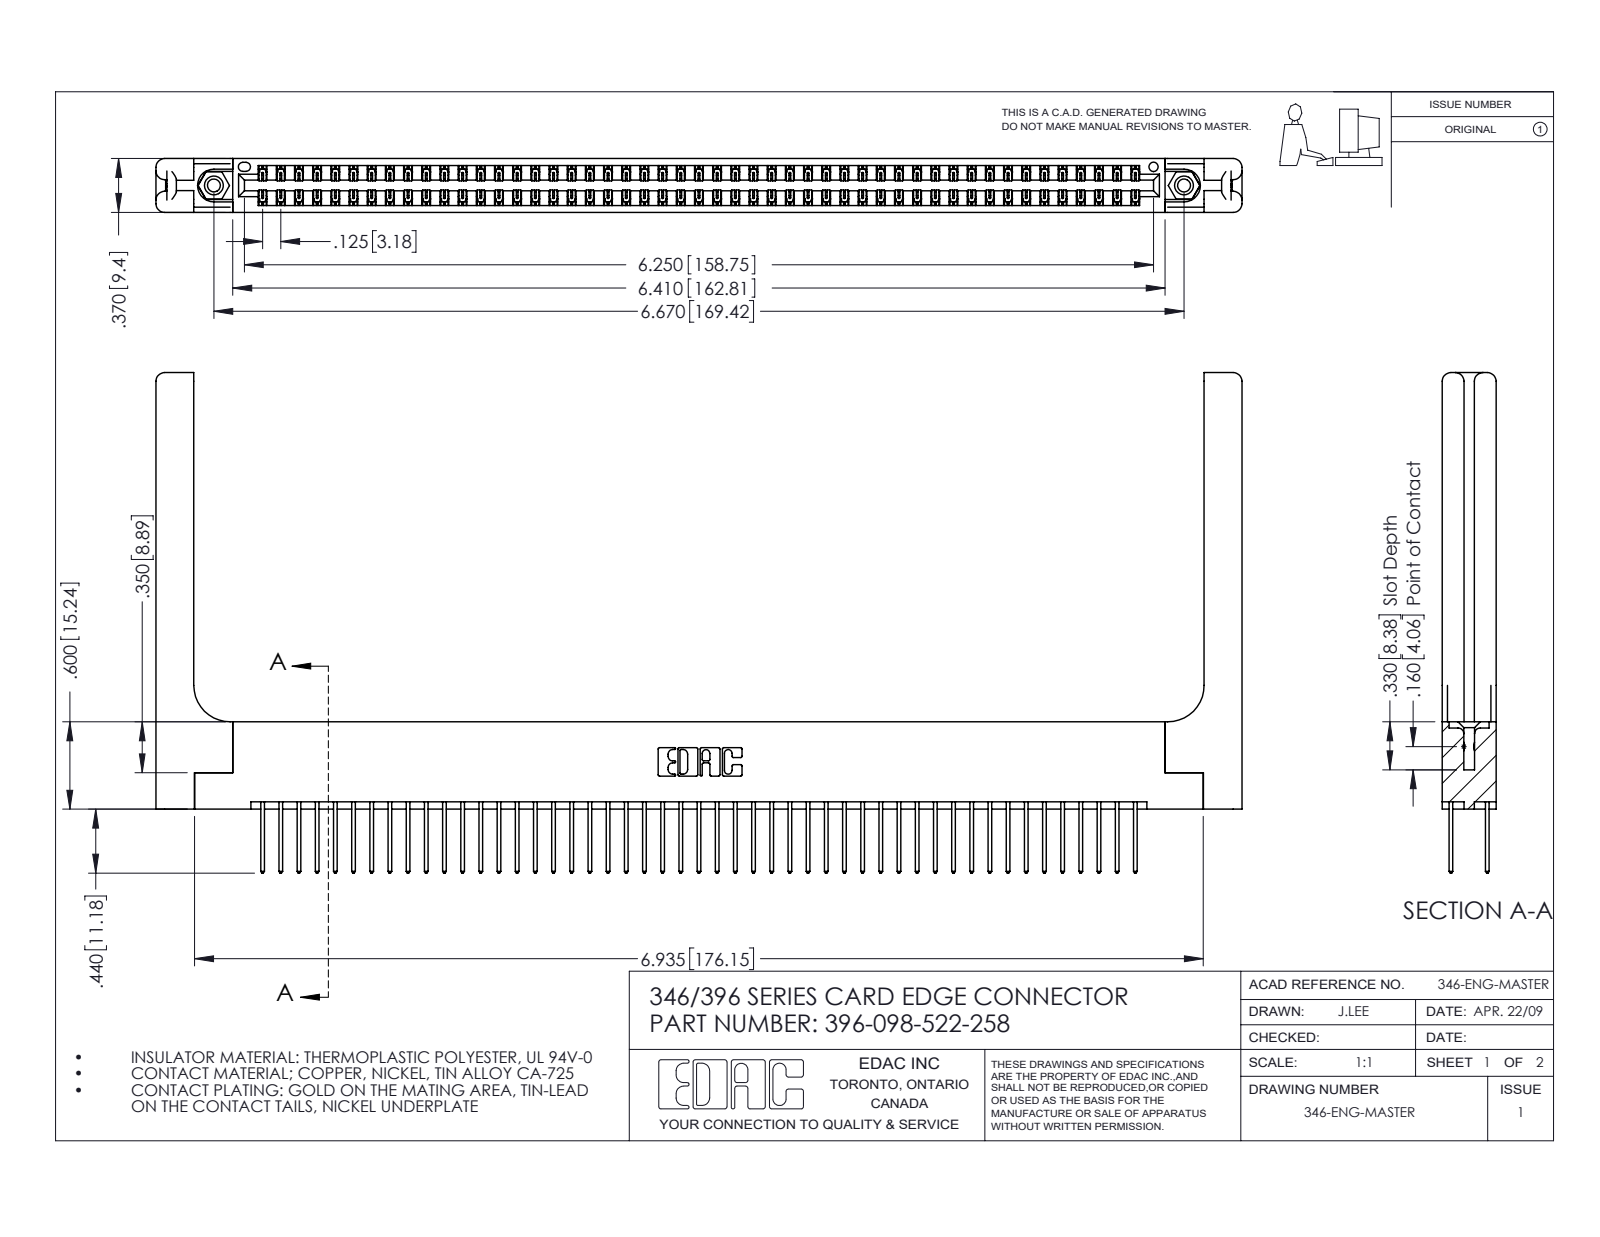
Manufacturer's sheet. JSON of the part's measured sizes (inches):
{"part_name": "346-220-058_345-220-058; 345-250-001_345-250-001-102; 346 Part_Flush Mounting Lugs - 0.156 Dia-TH; 396-098-522-258 (+1 more)", "step_written_by": "SolidWorks 2016 (CONFIG_CONTROL_DESIGN)", "units": "inches", "bodies": {"solids": 103, "faces": 5474, "planar": 3654, "cylindrical": 1760, "other": 60}, "overall_size": [7.466, 3.44, 0.37], "volume_in3": 1.604, "surface_area_in2": 49.73, "round_holes": [[0.089, 2], [0.125, 2], [0.156, 2], [0.064, 1]], "round_bosses_or_shafts": [[0.155, 2]], "partial_cylinders_radius": [[0.006, 147], [0.01, 98], [0.01, 22], [0.06, 16], [0.007, 6], [0.031, 6], [0.026, 3], [0.014, 2]], "face_to_face_distances": [0.048, 0.322, 0.37, 0.072, 0.25, 0.025, 0.298, 0.148, 0.15, 0.275], "hole_center_spacings": [0.246, 6.461, 6.67]}
